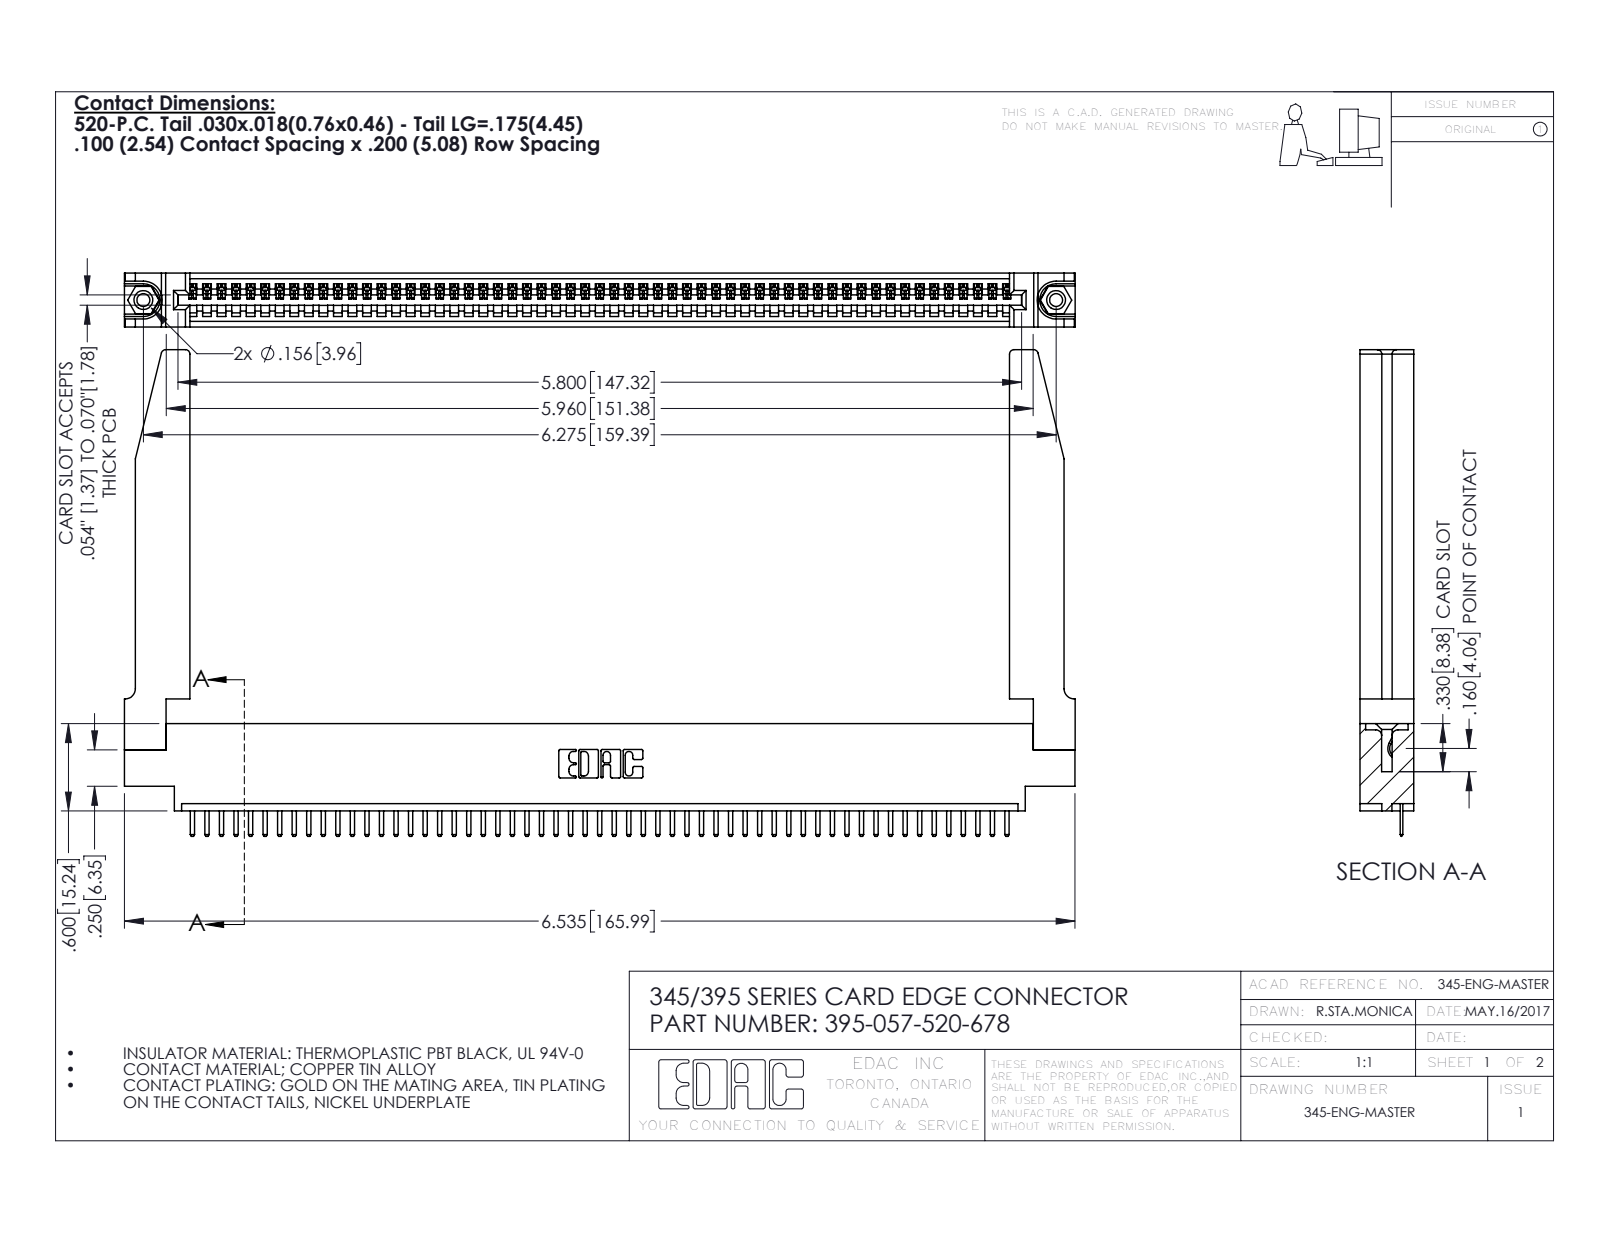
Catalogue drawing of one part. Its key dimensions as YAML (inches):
part_name: "345-220-078_345-220-078; 345-292-001_345-293-120; 345-250-001_345-250-001-102; 345 Part_0.170 Offset - 0.156 Dia-TH (+1 more)"
step_written_by: "SolidWorks 2016 (CONFIG_CONTROL_DESIGN)"
units: inches
bodies: {solids: 62, faces: 3898, planar: 2620, cylindrical: 1226, other: 52}
overall_size: [6.536, 3.345, 0.37]
volume: 1.427
surface_area: 42.45
round_holes:
  - {diameter: 0.089, count: 2}
  - {diameter: 0.125, count: 2}
  - {diameter: 0.156, count: 2}
  - {diameter: 0.064, count: 1}
round_bosses_or_shafts:
  - {diameter: 0.155, count: 2}
partial_cylinders:
  - {radius: 0.01, count: 116}
  - {radius: 0.006, count: 114}
  - {radius: 0.01, count: 22}
  - {radius: 0.03, count: 8}
  - {radius: 0.007, count: 6}
  - {radius: 0.031, count: 6}
  - {radius: 0.026, count: 3}
  - {radius: 0.031, count: 2}
face_to_face_distances: [0.37, 0.072, 0.298, 0.098, 0.272, 0.025, 0.2, 0.225, 0.072, 0.148]
hole_center_spacings: [0.27, 6.039, 6.275]
